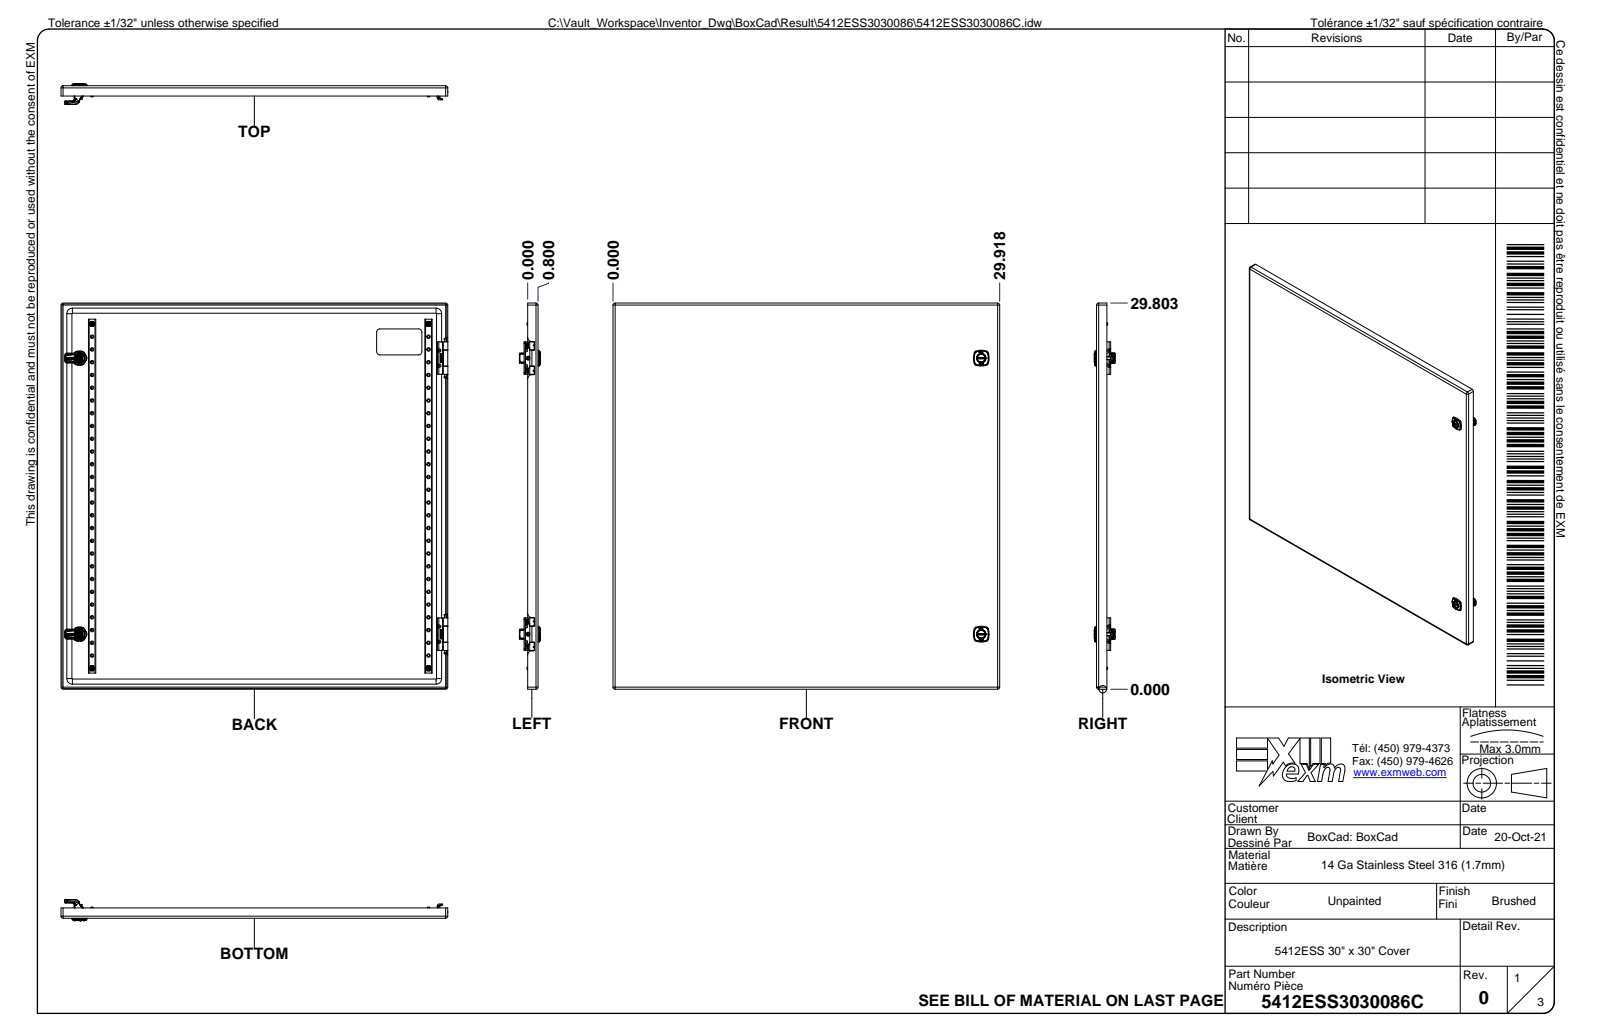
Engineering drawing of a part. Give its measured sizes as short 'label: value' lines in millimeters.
name: 5412ESS3030086; 5412ESS3030086B; 5412ESS3030086B-P; STK-Q-16020 (+8 more)
written by: Autodesk Inventor 2024 (AUTOMOTIVE_DESIGN)
unit: mm
bodies: 64 solids, 9382 faces (3057 planar, 1987 cylindrical, 4338 other)
size: 762.2 × 762 × 236
volume: 5 069 000 mm³; area: 5 274 000 mm²
holes: 52× ⌀4.2, 9× ⌀0.8, 8× ⌀5.1, 8× ⌀8, 6× ⌀7.4, 6× ⌀7.9, 4× ⌀1.1, 4× ⌀5, 4× ⌀6.8, 4× ⌀6.9, 4× ⌀9.9, 2× ⌀6
bosses: 52× ⌀6, 9× ⌀5.9, 9× ⌀0.8, 8× ⌀1, 4× ⌀18.2, 4× ⌀9.5, 4× ⌀7.9, 4× ⌀6.7
rounds: 106× R0.5, 68× R0.2, 62× R1, 34× R0.3, 34× R0.8, 28× R0.3, 24× R2.5, 20× R3.2
face distances: 1.7, 229.9, 760.3, 228.2, 231.6, 207.7, 23.9, 22.2, 206, 2.7
hole spacings: 25, 50, 75, 100, 125, 150, 695.9, 175
